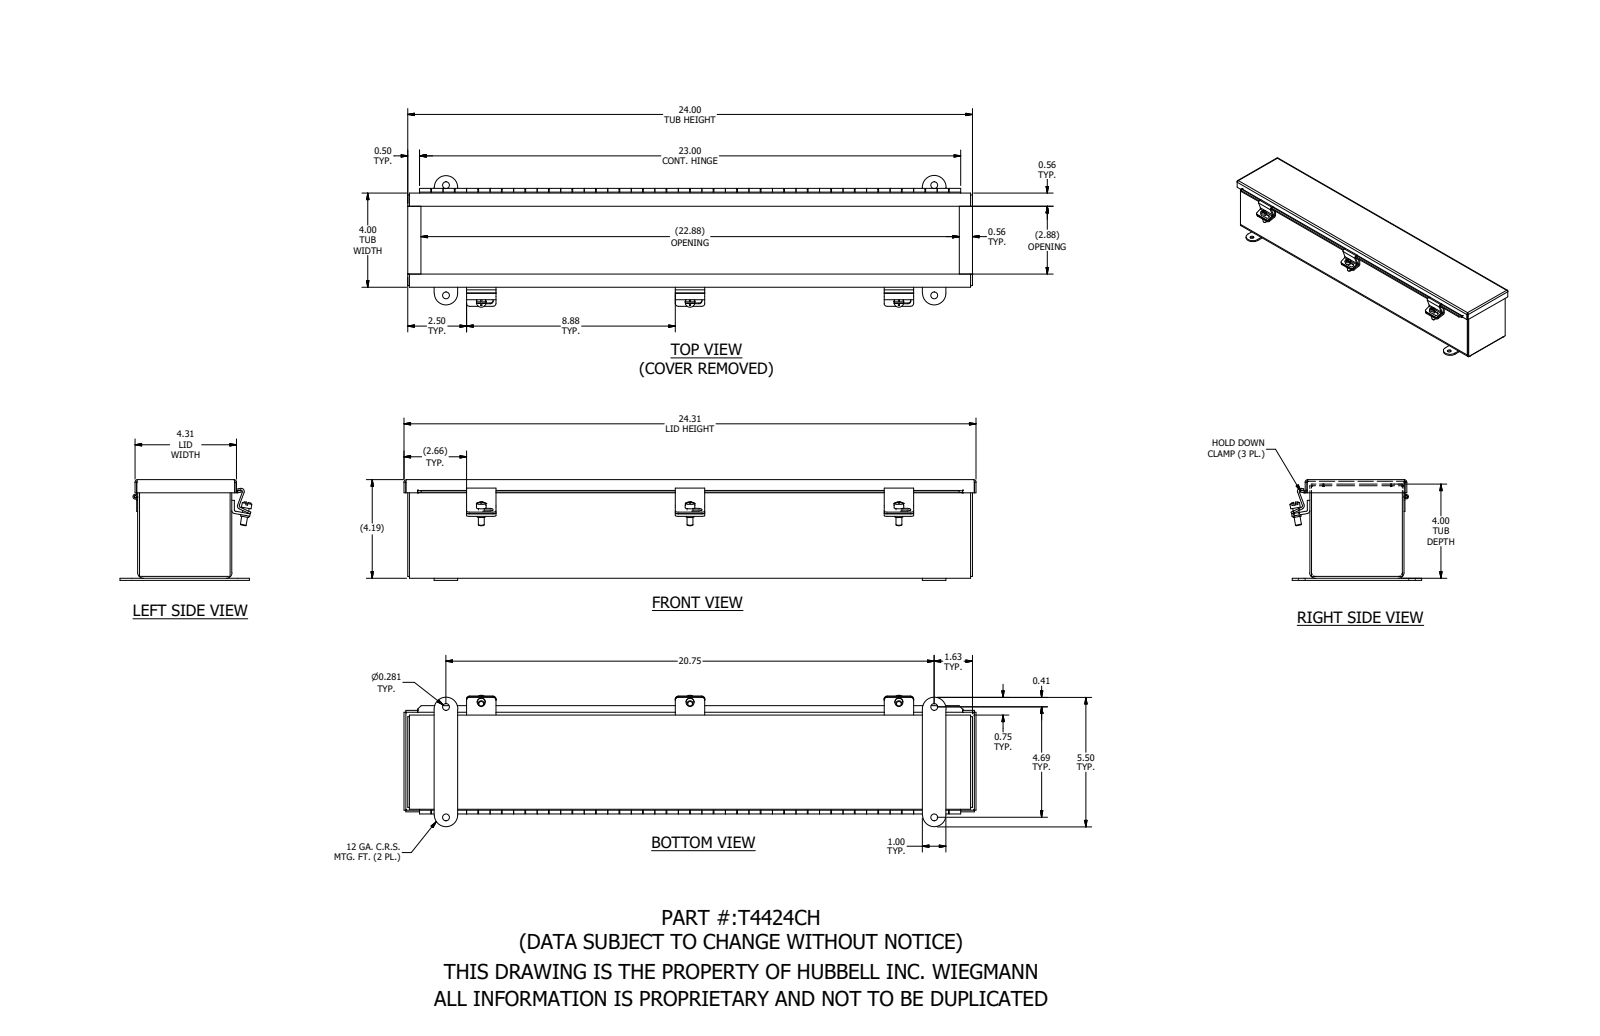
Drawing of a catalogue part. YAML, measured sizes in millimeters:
part_name: "T4424CH"
step_written_by: "SolidWorks 2021 (AUTOMOTIVE_DESIGN)"
units: millimeters
bodies: {solids: 18, faces: 646, planar: 338, cylindrical: 285, other: 23}
overall_size: [617.6, 142.1, 108.8]
volume: 627600
surface_area: 696100
round_holes:
  - {diameter: 7.1, count: 4}
  - {diameter: 5, count: 3}
  - {diameter: 2.9, count: 1}
round_bosses_or_shafts:
  - {diameter: 10.4, count: 3}
  - {diameter: 8.7, count: 3}
  - {diameter: 6.4, count: 3}
  - {diameter: 5.1, count: 1}
  - {diameter: 2.5, count: 1}
partial_cylinders:
  - {radius: 3.2, count: 12}
  - {radius: 0.8, count: 9}
  - {radius: 2.7, count: 9}
  - {radius: 3.4, count: 6}
  - {radius: 12.7, count: 4}
  - {radius: 1.6, count: 3}
  - {radius: 3.2, count: 3}
  - {radius: 4, count: 2}
face_to_face_distances: [1.9, 99.7, 104.5, 101.6, 97.8, 106.4, 102.6, 4.8, 102.7, 2.9]
hole_center_spacings: [119, 527.1, 540.3, 225.4, 225.4, 450.9]
